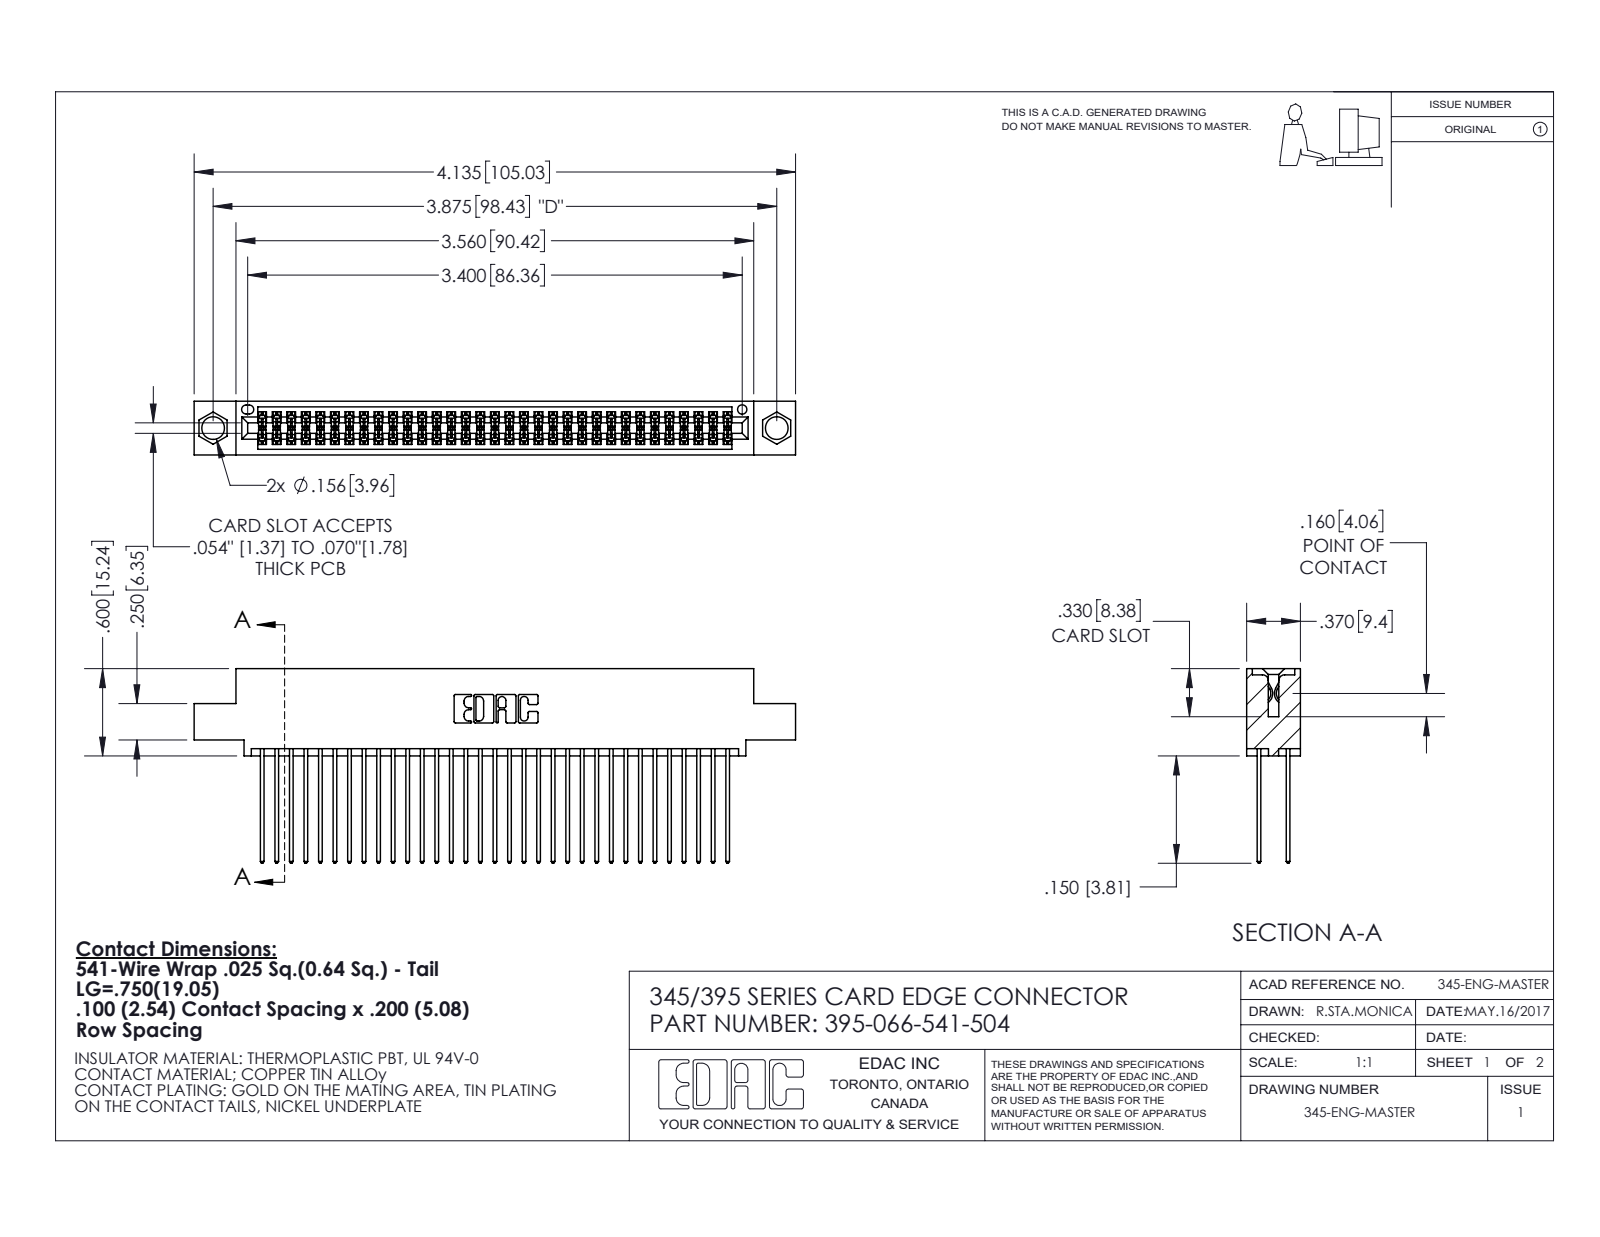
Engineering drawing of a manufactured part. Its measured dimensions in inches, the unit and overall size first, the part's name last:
Units: inches
Overall size (bounding box): 4.135 × 1.337 × 0.37
Round holes (diameter × count): ⌀0.156 ×2, ⌀0.064 ×1
Partial cylindrical surfaces — rounded edges, fillets, slot ends (radius × count): R0.006 ×132, R0.01 ×66, R0.01 ×22, R0.007 ×6, R0.031 ×6, R0.026 ×3, R0.014 ×2, R0.019 ×2
Main face-to-face distances: 0.072, 0.298, 0.2, 0.098, 0.272, 0.025, 0.225, 0.37, 0.175, 0.149
Hole centre spacings: 0.27, 3.64, 3.875
Volume: 0.63 in³ · Surface area: 26.04 in²
Bodies: 67 solids, 3444 faces (2276 planar, 1168 cylindrical, 0 other)
Part name (STEP PRODUCT): 345-292-001_345-293-141; 395-066-541-504; 345 Part_0.110 Offset - 0.156 Dia-TI
STEP written by: SolidWorks 2020 (CONFIG_CONTROL_DESIGN)
